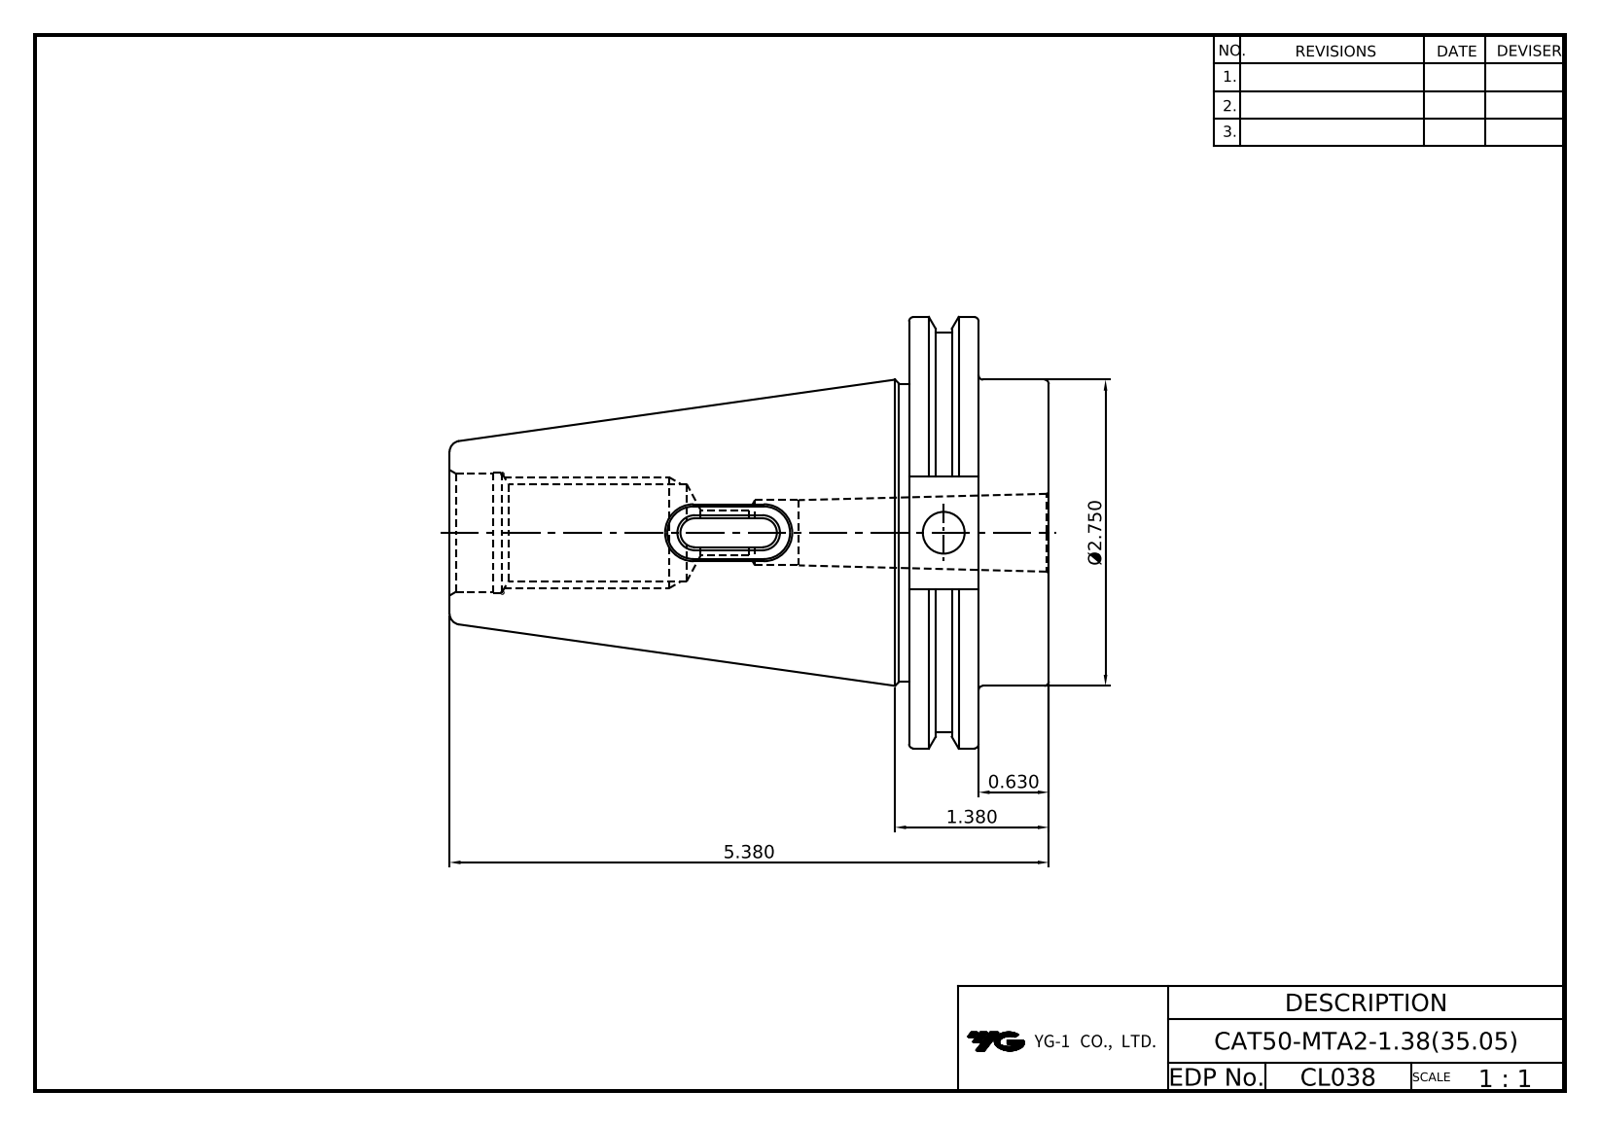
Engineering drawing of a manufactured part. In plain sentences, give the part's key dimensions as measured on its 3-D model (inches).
The part is named "LO-CAT50-MTA2-35.05". Its 3-D file was written by "Autodesk Inventor 2025 (AUTOMOTIVE_DESIGN)". It is 1 solid with 100 faces: 41 planar, 23 cylindrical and 36 other. Overall it measures 5.38 by 3.875 by 3.728 inches. Its volume is 23.24 cubic inches and its surface area 75.96 square inches. Round holes: 1 of diameter 0.375, 1 of diameter 0.406, 1 of diameter 0.587, 1 of diameter 0.865, 1 of diameter 1.031. Round bosses or shafts: 1 of diameter 3.875, 1 of diameter 3.594, 1 of diameter 2.75, 1 of diameter 2.726. Partial cylindrical surfaces (rounded edges, fillets, slot ends): 2 of radius 0.124, 2 of radius 0.236. The main face-to-face distances are 1.255, 0.625, 0.63, 0.274, 0.746, 0.386, 0.634, 0.112, 0.36, 4.125.
